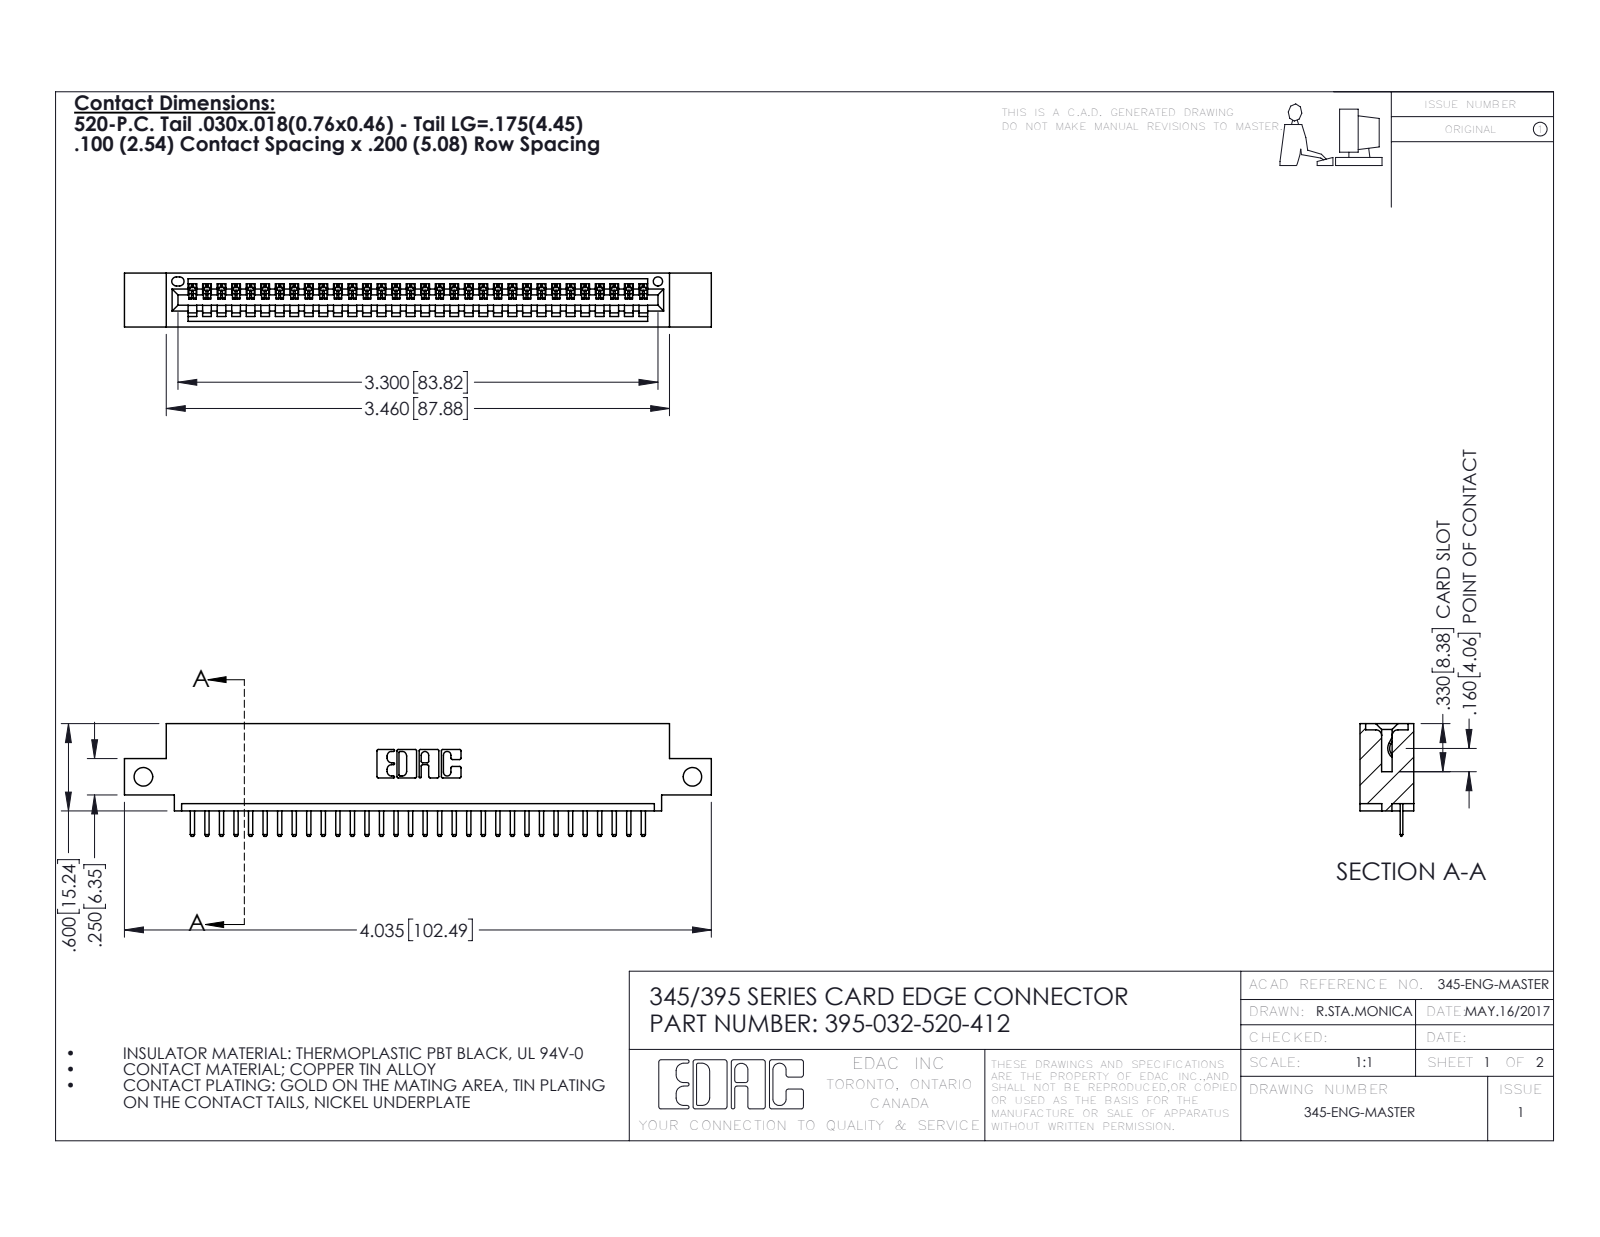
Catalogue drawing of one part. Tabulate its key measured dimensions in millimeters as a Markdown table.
| quantity | value |
| --- | --- |
| part name | 395-032-520-412; 345-292-001_345-293-120; 345 Part_0.110 Offset - Side Mount |
| STEP written by | SolidWorks 2016 (CONFIG_CONTROL_DESIGN) |
| units | millimeters |
| bodies | 33 solids, 2114 faces (1428 planar, 686 cylindrical, 0 other) |
| overall size | 102.5 × 19.7 × 9.4 |
| volume | 9 410 mm³ |
| surface area | 11 990 mm² |
| round holes (diameter × count) | 3.3 × 2, 1.6 × 1 |
| partial cylindrical surfaces (radius × count) | 0.3 × 66, 0.2 × 64, 0.3 × 22, 0.2 × 6, 0.8 × 6, 0.7 × 3, 0.8 × 2, 1 × 2 |
| main face-to-face distances | 7.6, 1.8, 9.4, 5.1, 2.5, 6.9, 0.6, 5.7, 1.8, 3.8 |
| hole center spacings | 95.9 |
